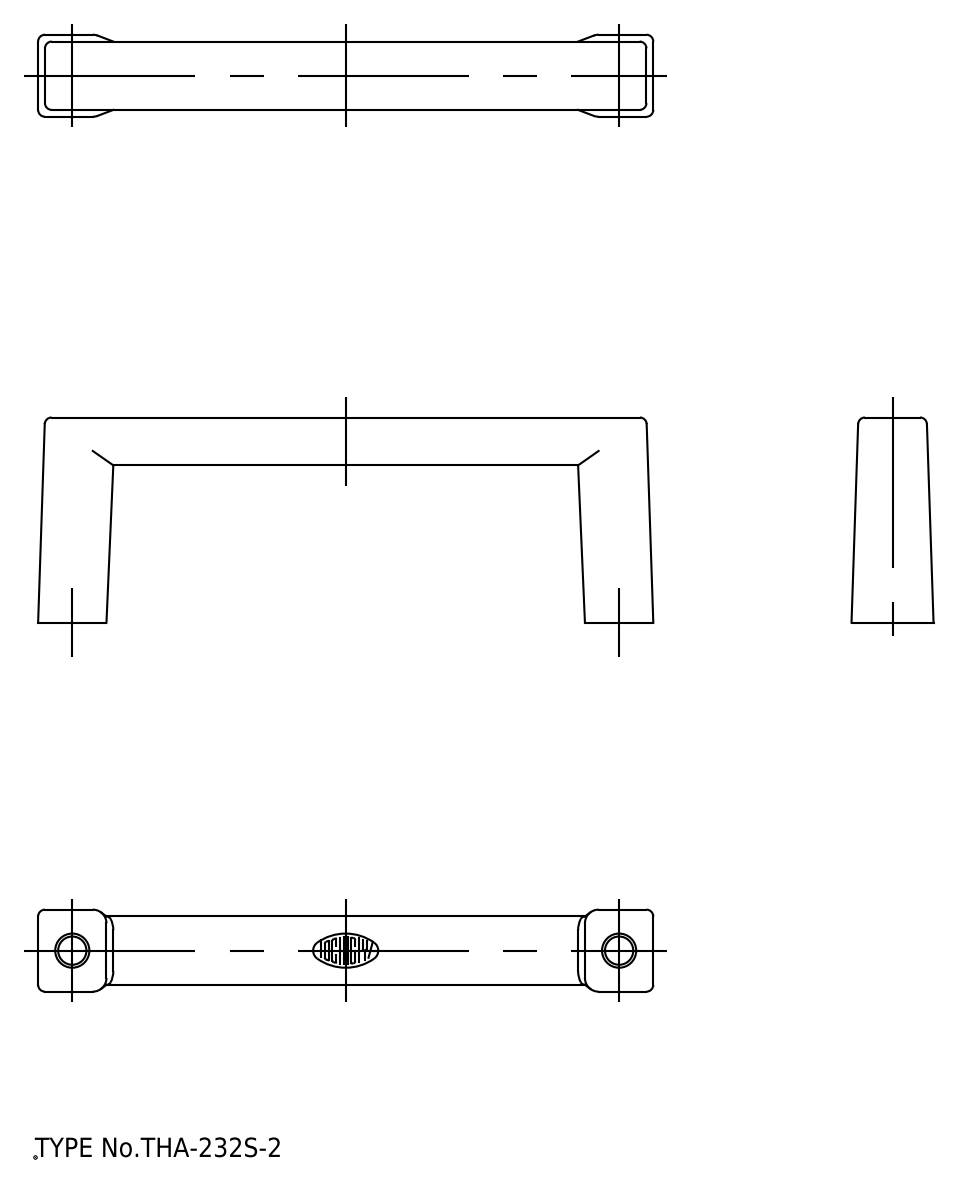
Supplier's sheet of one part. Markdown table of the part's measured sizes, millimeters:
| quantity | value |
| --- | --- |
| STEP written by | spGate 19.8.4 (****-****-****-****) (AUTOMOTIVE_DESIGN) |
| units | millimeters |
| bodies | 1 solid, 34 faces (12 planar, 18 cylindrical, 4 other) |
| overall size | 90 × 30 × 12 |
| volume | 10 802 mm³ |
| surface area | 5 216 mm² |
| round holes (diameter × count) | 5 × 2 |
| partial cylindrical surfaces (radius × count) | 1 × 8, 2 × 6 |
| main face-to-face distances | 7, 23, 30, 12, 11, 18 |
| hole center spacings | 80 |
